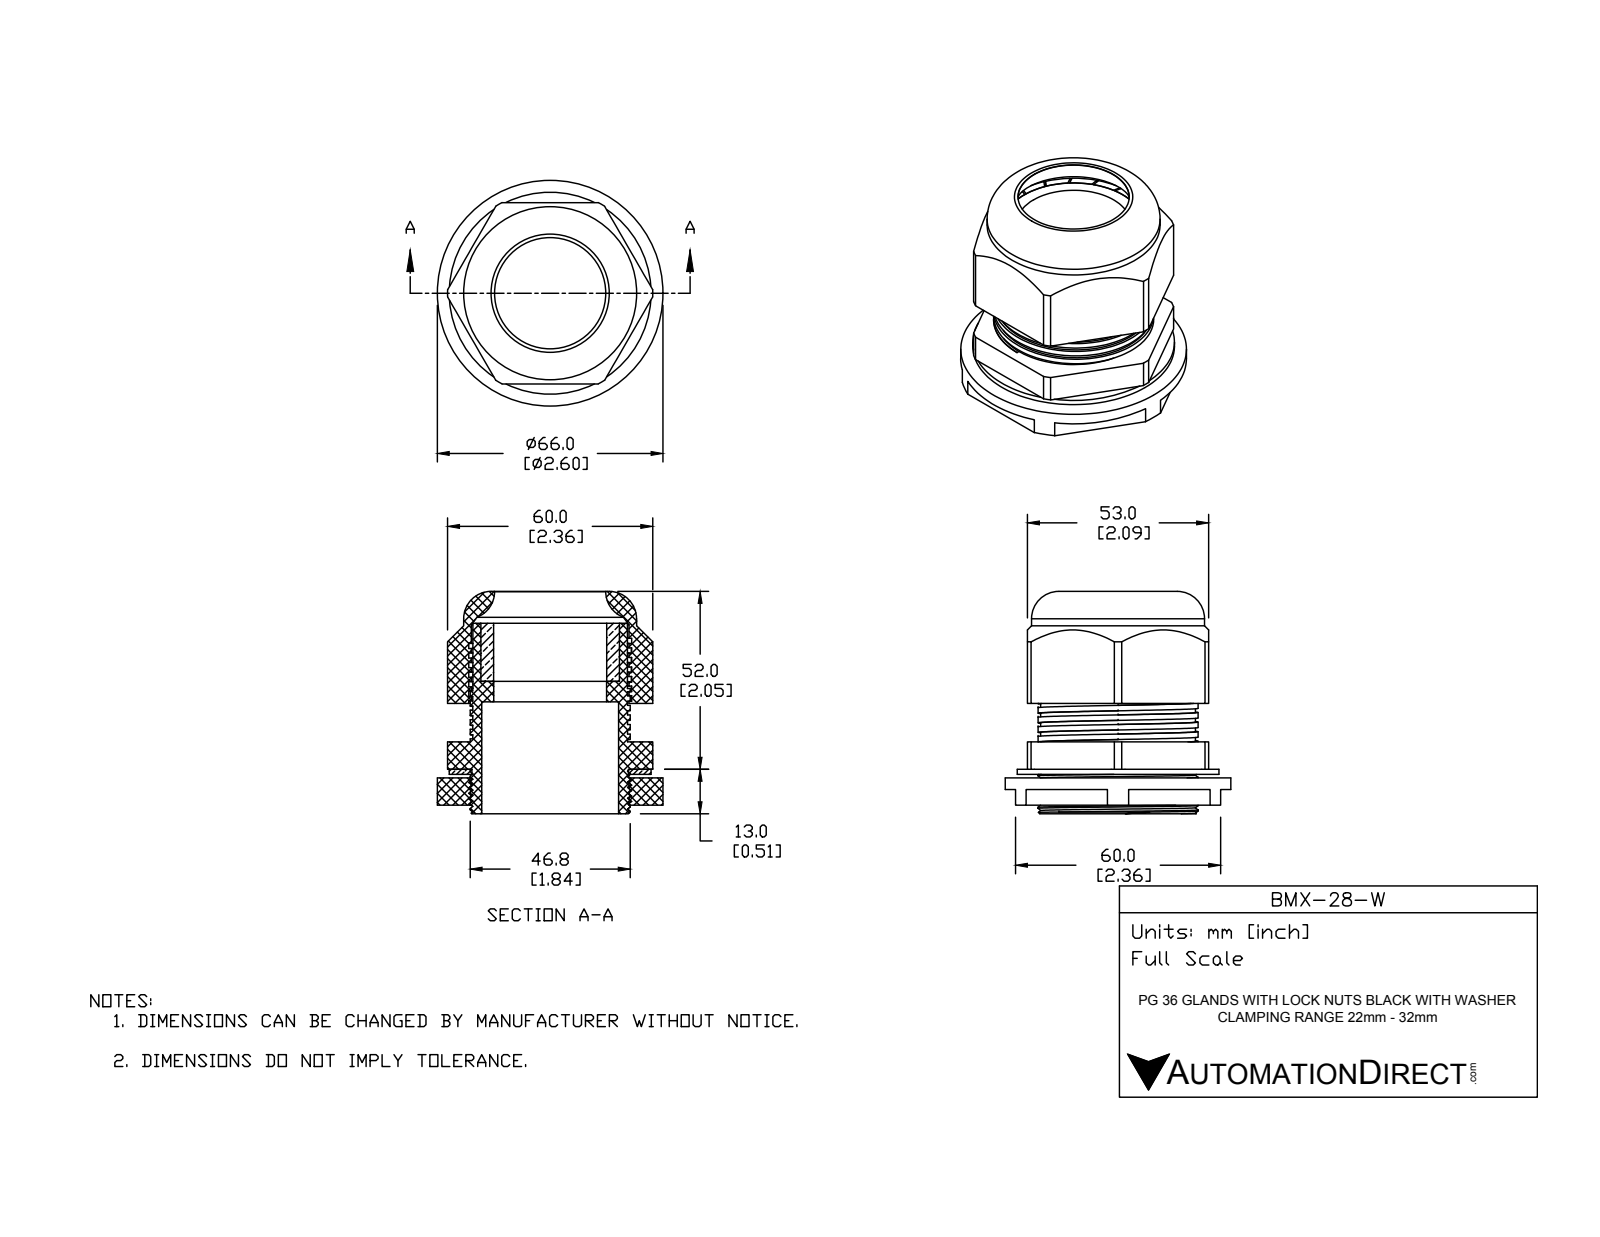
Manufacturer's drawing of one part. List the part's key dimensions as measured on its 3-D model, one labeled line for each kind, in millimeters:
Part name (STEP PRODUCT): BMX-28-W
STEP written by: SolidWorks 2015 (CONFIG_CONTROL_DESIGN)
Units: millimetres
Bodies: 5 solids, 223 faces (111 planar, 91 cylindrical, 21 other)
Overall size (bounding box): 66 × 66 × 65
Volume: 72 781 mm³ · Surface area: 49 179 mm²
Round holes (diameter × count): ⌀32.5 ×1, ⌀33 ×1, ⌀33.1 ×1, ⌀40 ×1, ⌀40.5 ×1, ⌀45.8 ×1, ⌀46.13 ×1
Round bosses / shafts (diameter × count): ⌀66 ×1, ⌀59 ×1, ⌀50.6 ×1, ⌀46.8 ×1, ⌀45.2 ×1
Partial cylindrical surfaces — rounded edges, fillets, slot ends (radius × count): R30 ×1
Main face-to-face distances: 10.5, 53, 8, 2.5, 9, 1, 1.5, 36.2, 28.2, 27.2
